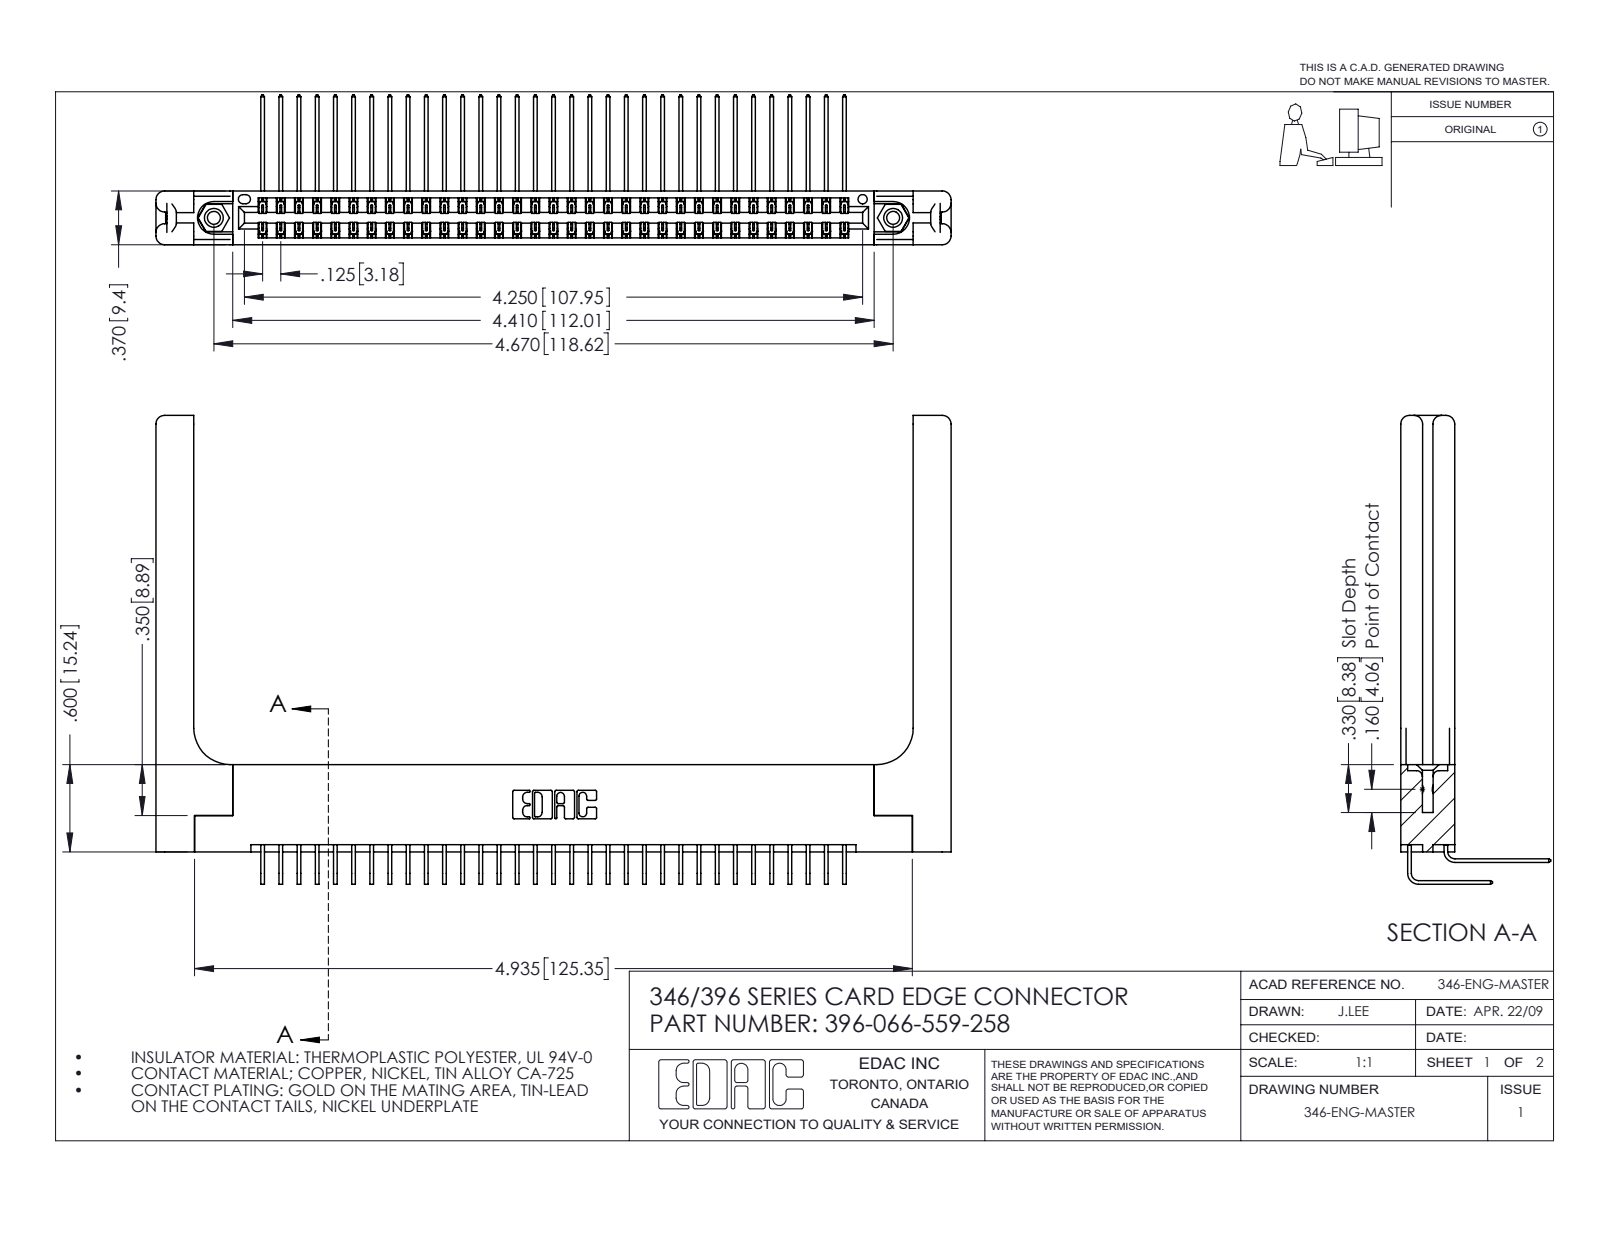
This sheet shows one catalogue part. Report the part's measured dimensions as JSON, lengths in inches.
{"part_name": "346 Part_Flush Mounting Lugs - 0.156 Dia-TH; 345-250-001_345-250-001-102; 345-292-001_559 Tail - 2; 345-292-001_558 559 Tail - 1 (+2 more)", "step_written_by": "SolidWorks 2016 (CONFIG_CONTROL_DESIGN)", "units": "inches", "bodies": {"solids": 71, "faces": 3942, "planar": 2666, "cylindrical": 1216, "other": 60}, "overall_size": [5.466, 3.223, 1.03], "volume_in3": 1.302, "surface_area_in2": 39.83, "round_holes": [[0.089, 2], [0.125, 2], [0.156, 2], [0.064, 1]], "round_bosses_or_shafts": [[0.155, 2]], "partial_cylinders_radius": [[0.006, 99], [0.01, 22], [0.06, 16], [0.007, 6], [0.031, 6], [0.026, 3], [0.014, 2], [0.022, 2]], "face_to_face_distances": [0.048, 0.37, 0.322, 0.072, 0.025, 0.148, 0.15, 0.25, 0.298, 0.275], "hole_center_spacings": [0.246, 4.462, 4.67]}
